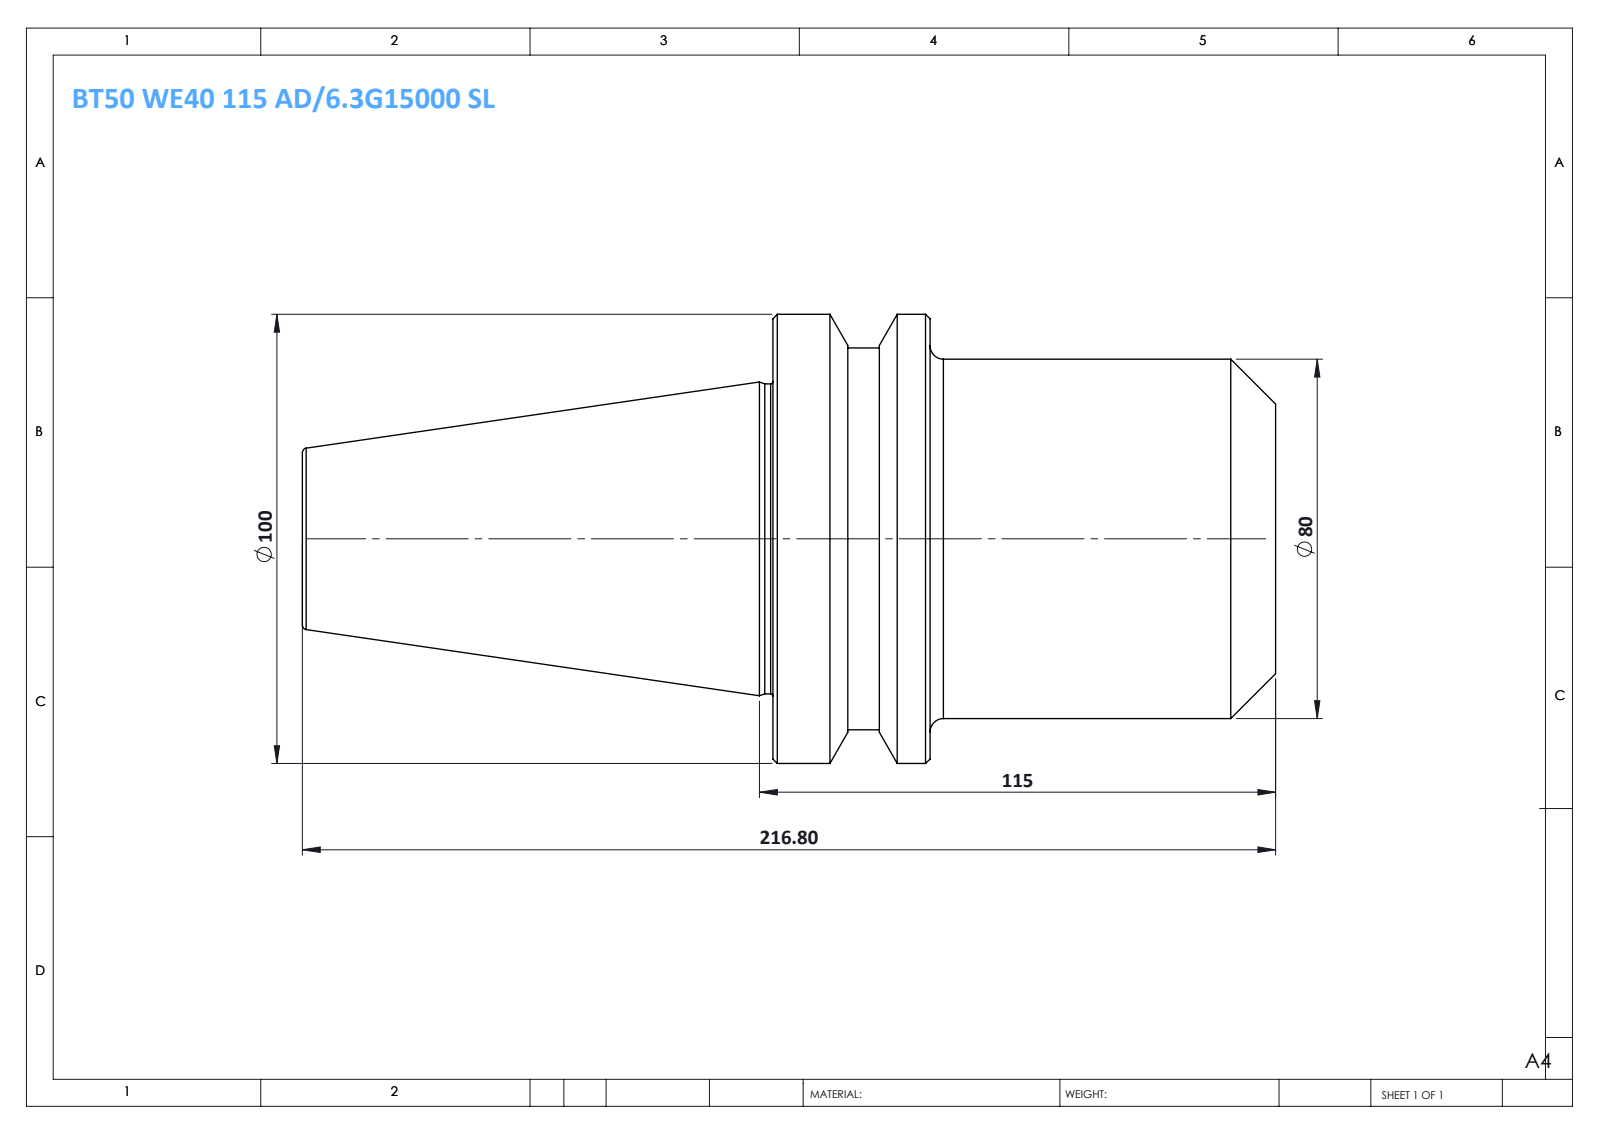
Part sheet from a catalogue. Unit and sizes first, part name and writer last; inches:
Units: inches
Overall size (bounding box): 8.535 × 3.937 × 3.937
Round bosses / shafts (diameter × count): ⌀3.937 ×1, ⌀3.346 ×1, ⌀3.15 ×1, ⌀2.717 ×1
Main face-to-face distances: 4.409, 3.031, 1.378, 8.535, 5.504, 4.126, 3.476, 0.445, 0.933, 5.059
Volume: 54.07 in³ · Surface area: 95.78 in²
Bodies: 1 solid, 36 faces (6 planar, 10 cylindrical, 20 other)
Part name (STEP PRODUCT): BT50 WE40 115 AD-6.3G15000 SL
STEP written by: SolidWorks 2014 (CONFIG_CONTROL_DESIGN)
